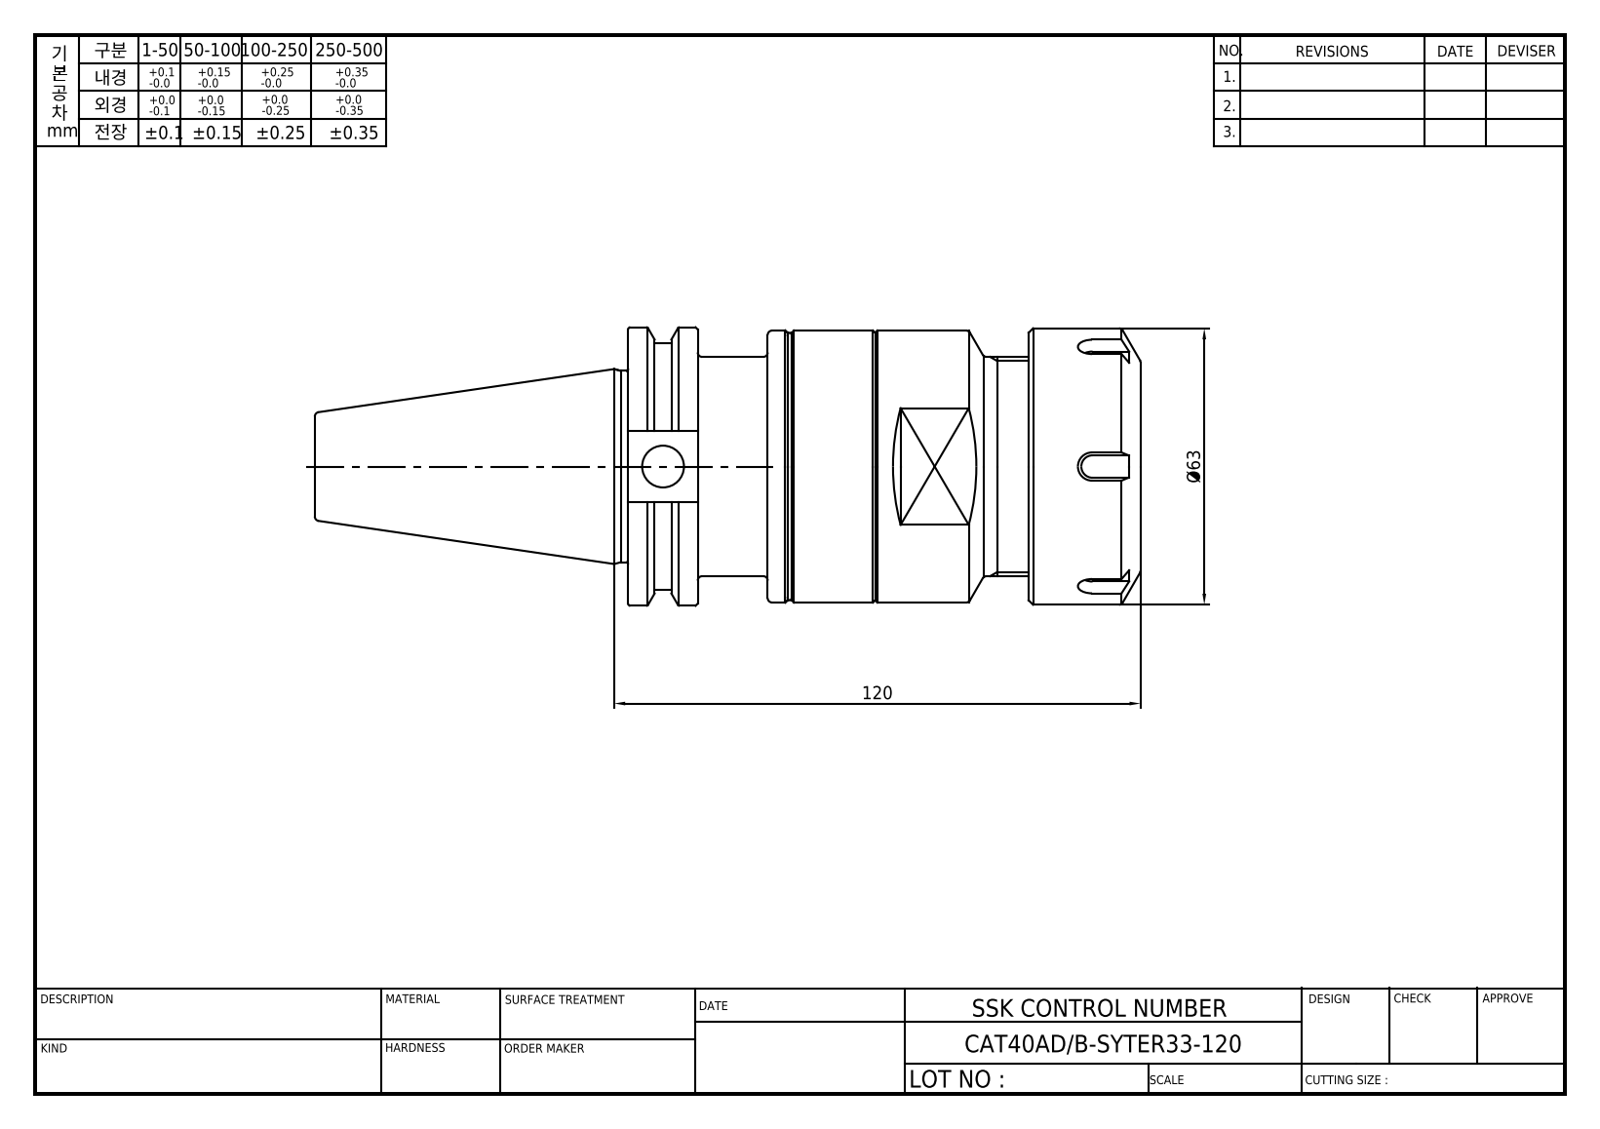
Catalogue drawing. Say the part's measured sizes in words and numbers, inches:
The part is named "LO-CAT40ADB-SYTER33-120; SYTER33-COVER(BLUE); SYNCHRO-ER40-60; ER40NUT". Its 3-D file was written by "Autodesk Inventor 2025 (AUTOMOTIVE_DESIGN)". It is 4 solids with 261 faces: 100 planar, 76 cylindrical and 85 other. Overall it measures 7.411 by 2.5 by 2.48 inches. Its volume is 18.32 cubic inches and its surface area 117.4 square inches. Round holes: 4 of diameter 0.128, 4 of diameter 0.315, 4 of diameter 0.319, 2 of diameter 0.157, 2 of diameter 0.165, 1 of diameter 0.056, 1 of diameter 0.262, 1 of diameter 0.335, 1 of diameter 0.375, 1 of diameter 0.527, 1 of diameter 0.642, 1 of diameter 0.881. Round bosses or shafts: 1 of diameter 2.5, 1 of diameter 2.48, 1 of diameter 2.441, 1 of diameter 2.283, 1 of diameter 2.181, 1 of diameter 1.969, 1 of diameter 1.957, 1 of diameter 1.717. Partial cylindrical surfaces (rounded edges, fillets, slot ends): 12 of radius 0.02, 1 of radius 0.322, 1 of radius 1.108. The main face-to-face distances are 1.976, 0.031, 1.619, 1.651, 0.398, 4.6, 2.98, 2.949, 3.596, 1.945. The hole center spacings are 0.748, 1.496, 0.019, 1.044, 1.057, 1.058, 1.071, 1.496.
